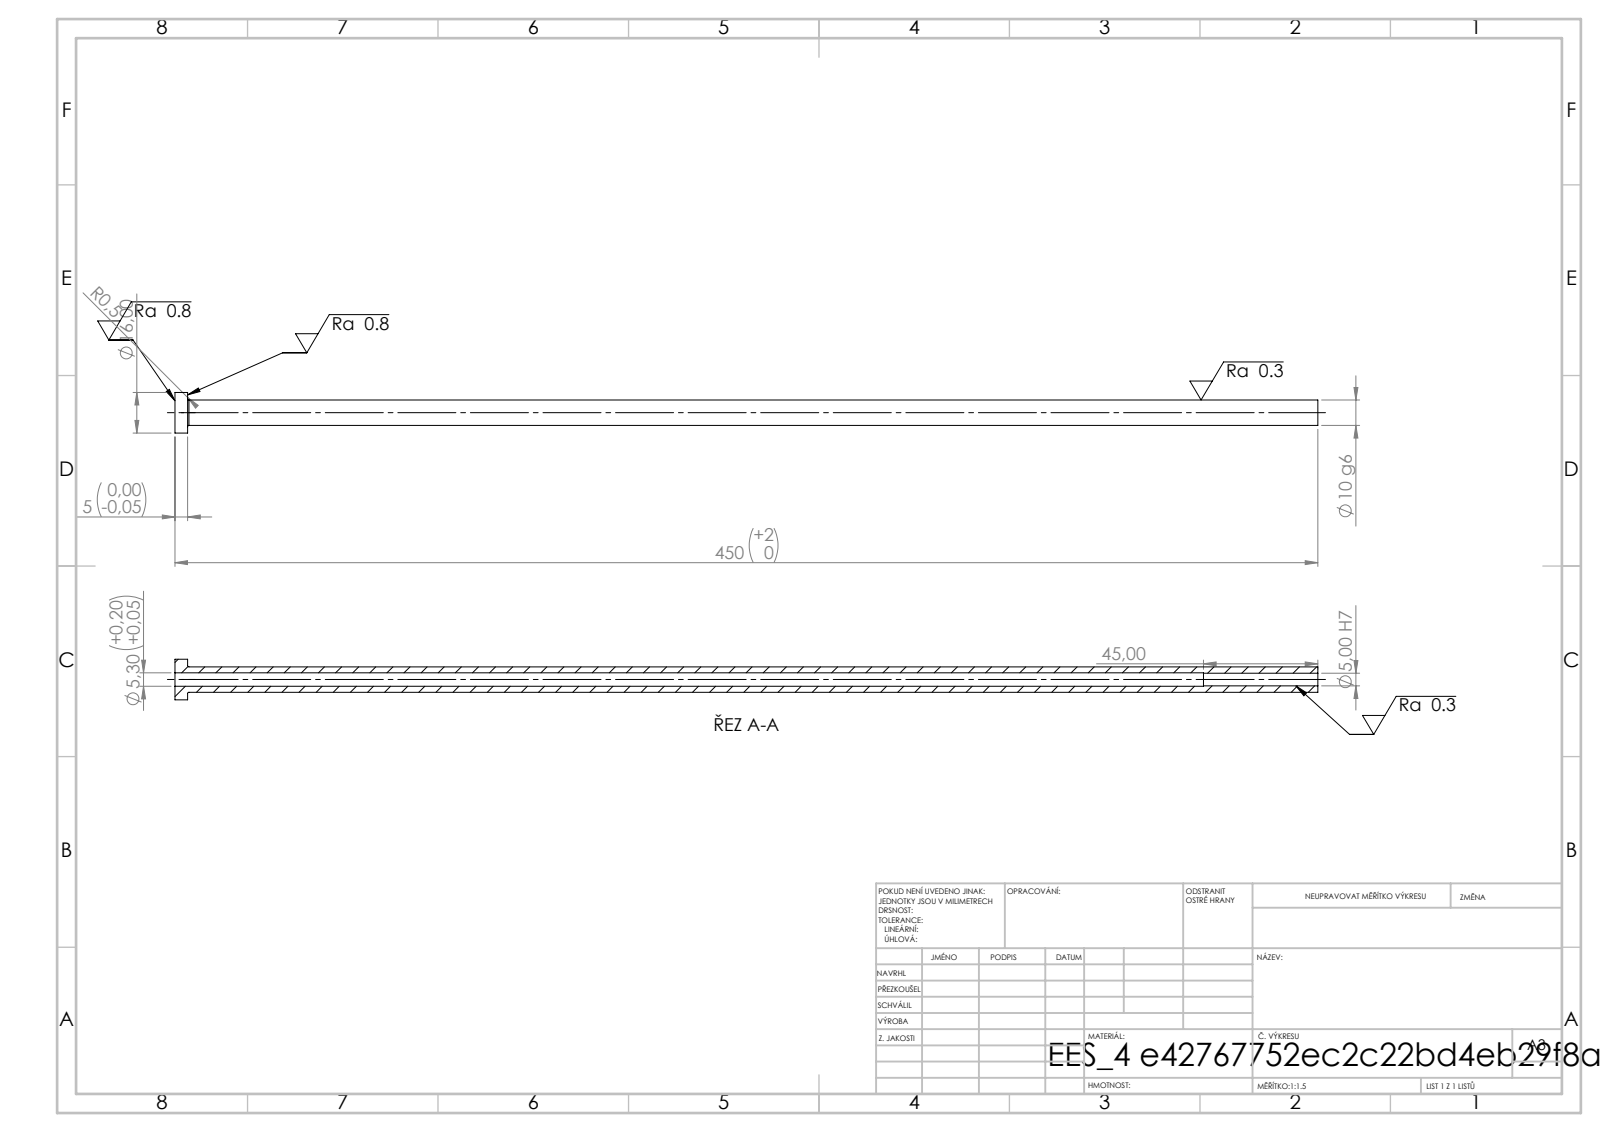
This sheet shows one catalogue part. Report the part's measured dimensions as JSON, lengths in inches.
{"step_written_by": "SolidWorks 2019 (CONFIG_CONTROL_DESIGN)", "units": "inches", "bodies": {"solids": 1, "faces": 14, "planar": 4, "cylindrical": 8, "other": 2}, "overall_size": [17.717, 0.63, 0.63], "volume_in3": 1.595, "surface_area_in2": 34.16, "round_holes": [[0.197, 1], [0.209, 1]], "round_bosses_or_shafts": [[0.63, 1], [0.394, 1]], "face_to_face_distances": [0.197, 17.717, 17.52, 15.945, 15.748, 1.772]}
